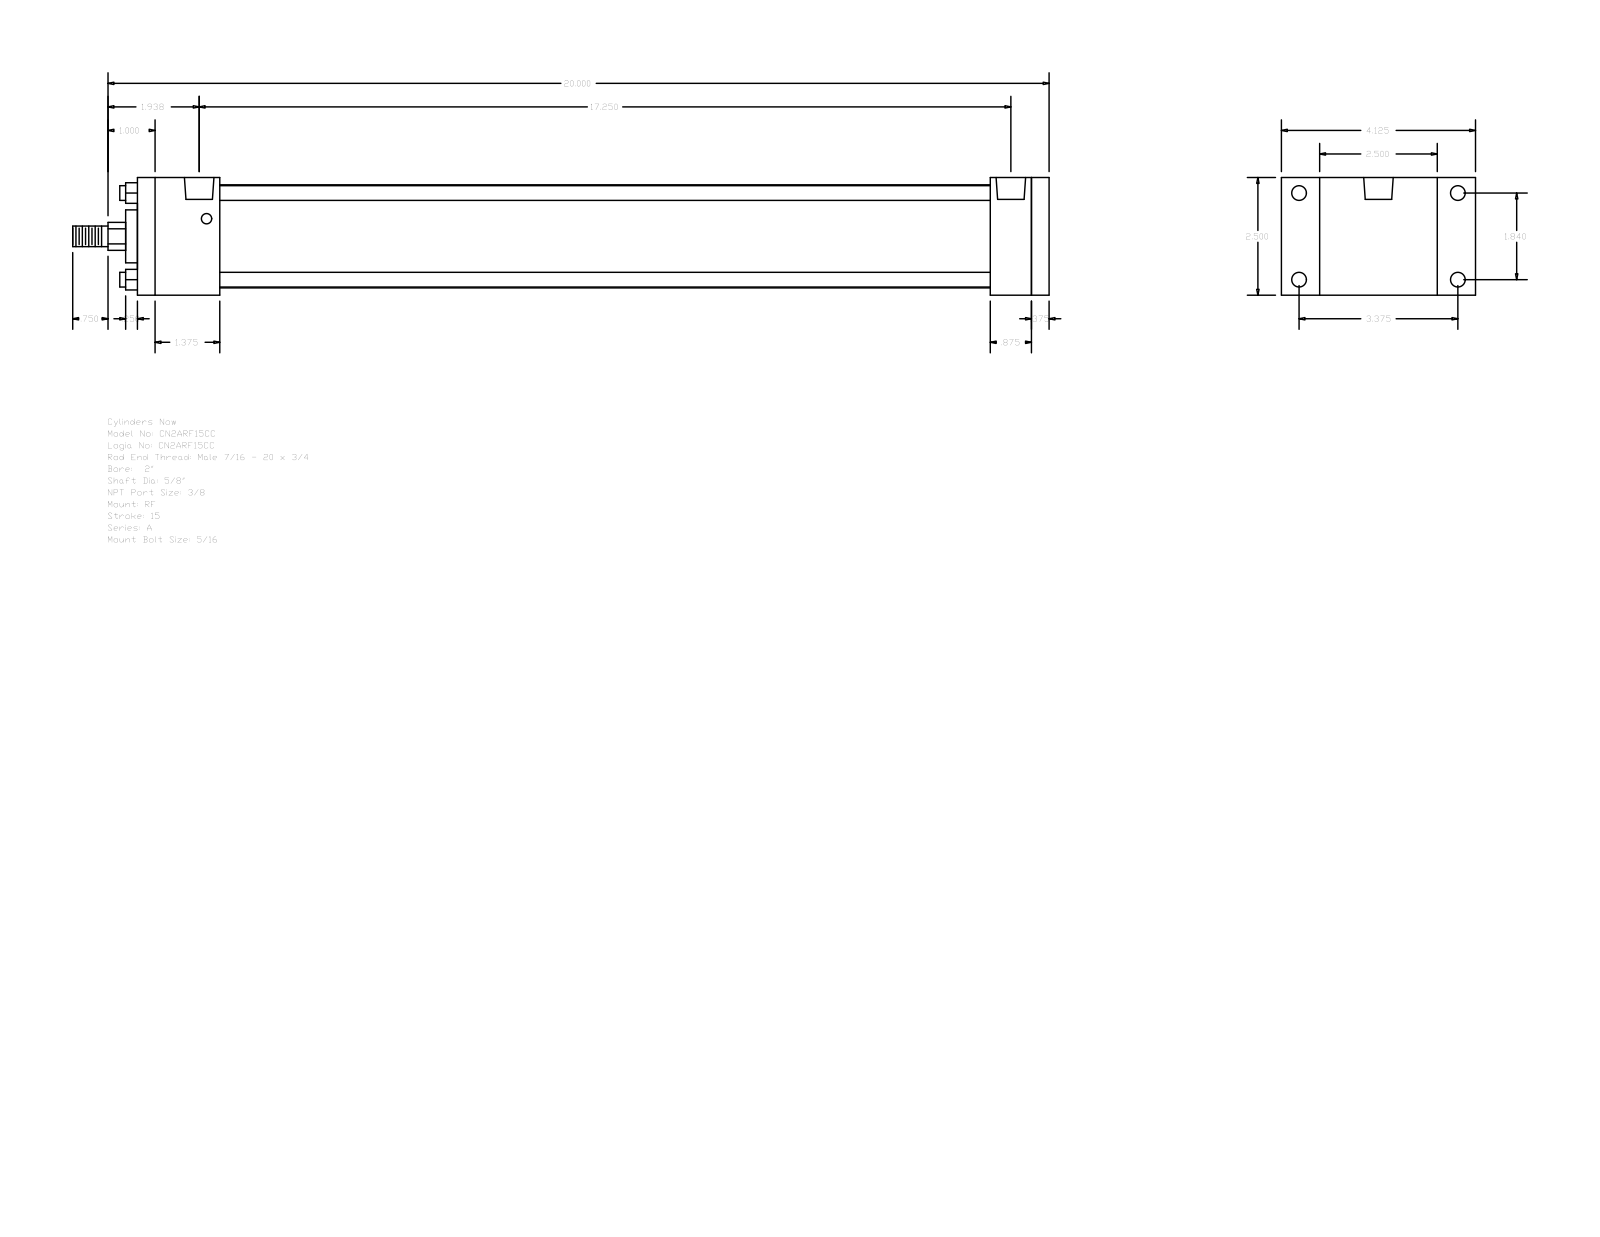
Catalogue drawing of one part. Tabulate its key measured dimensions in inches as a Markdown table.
| quantity | value |
| --- | --- |
| part name | A_RF__0200_0.625 |
| STEP written by | GSSL Pune (CONFIG_CONTROL_DESIGN) |
| units | inches |
| bodies | 0 solids, 92 faces (64 planar, 28 cylindrical, 0 other) |
| overall size | 20.75 × 4.125 × 2.5 |
| round holes (diameter × count) | 0.219 × 4, 0.313 × 4, 0.627 × 2 |
| round bosses / shafts (diameter × count) | 0.313 × 4, 2.19 × 1, 1.125 × 1, 0.625 × 1, 0.437 × 1 |
| partial cylindrical surfaces (radius × count) | 0.297 × 1 |
| main face-to-face distances | 2.5, 19.375, 19, 0.375, 1.75, 17.25, 17.625, 18.125, 16.375, 0.875 |
| hole center spacings | 1.84, 3.375, 3.844, 16.937, 0.156, 0.157, 17.093, 17.094 |
